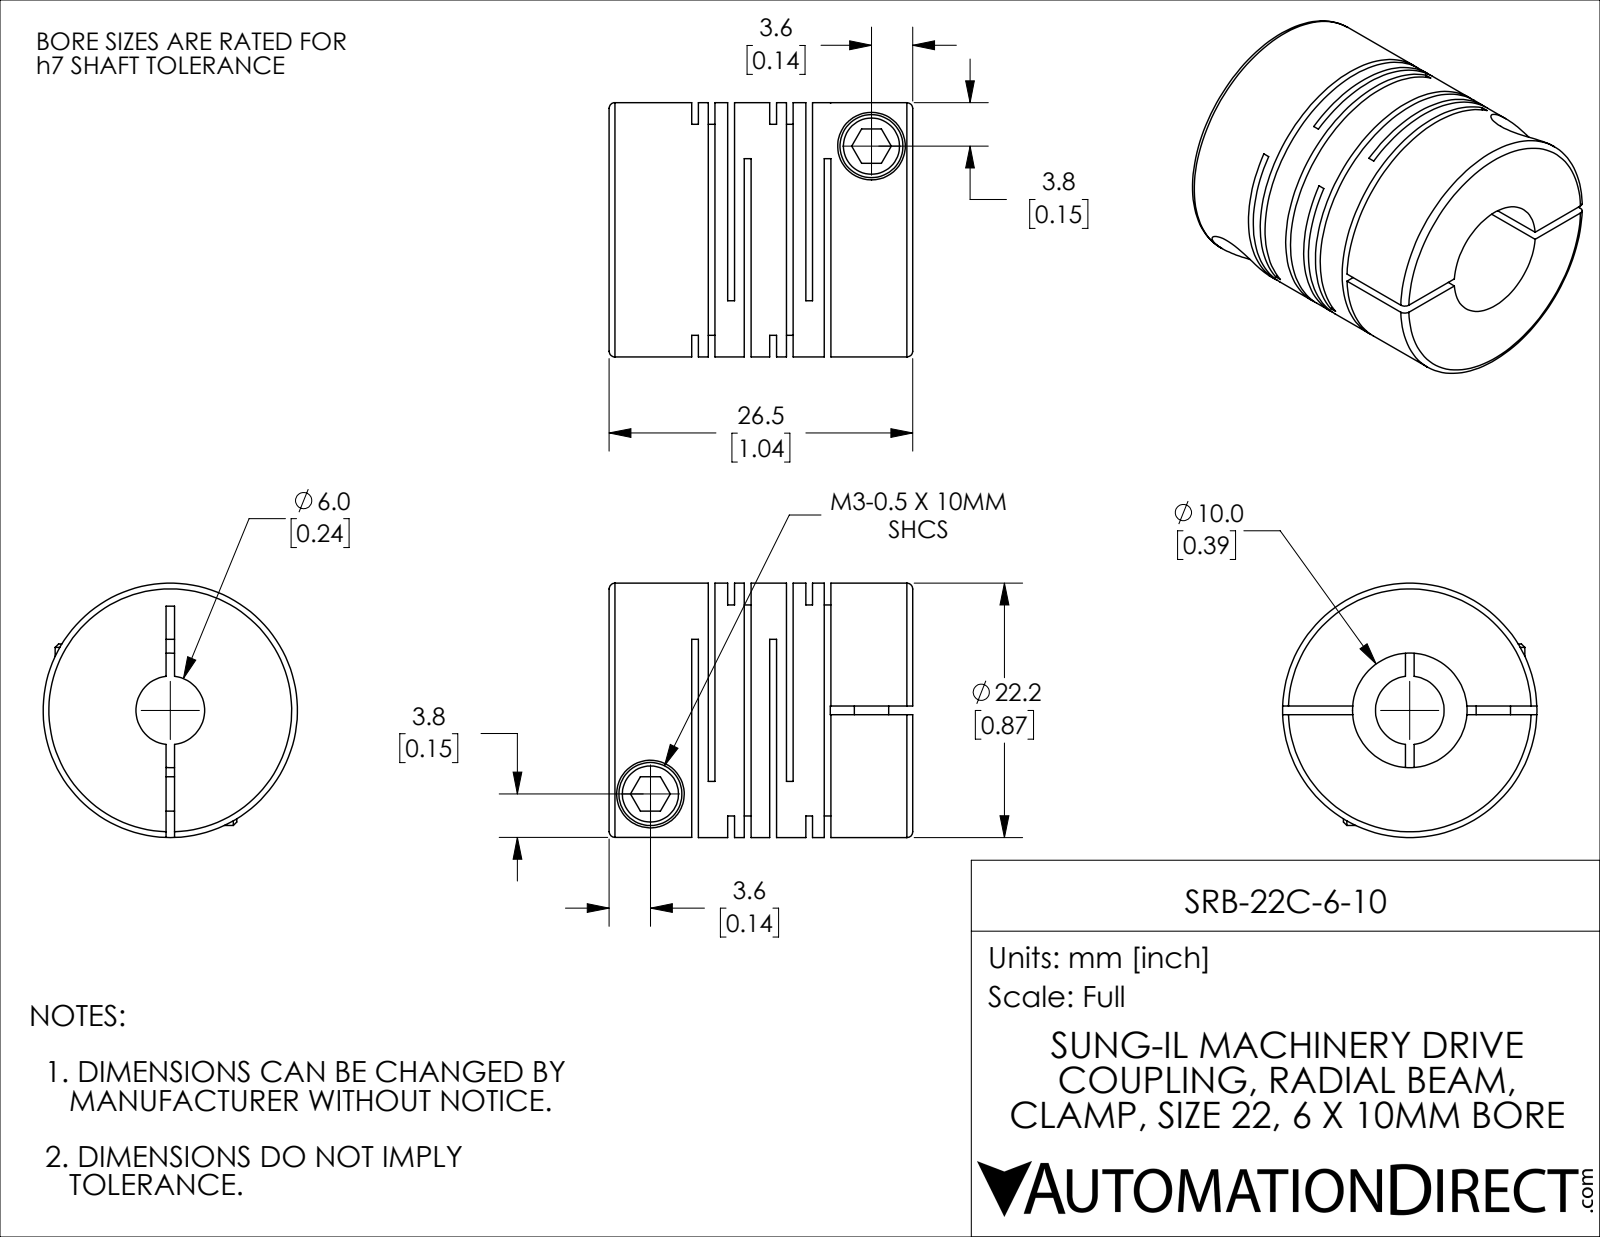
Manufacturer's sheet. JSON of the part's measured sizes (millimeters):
{"part_name": "SRB-22C-6-10", "step_written_by": "SolidWorks 2021 (CONFIG_CONTROL_DESIGN)", "units": "millimeters", "bodies": {"solids": 1, "faces": 115, "planar": 60, "cylindrical": 42, "other": 13}, "overall_size": [26.5, 22.2, 22.2], "volume_mm3": 7057, "surface_area_mm2": 7498, "round_holes": [[3, 2], [5.9, 2], [6, 1], [10, 1]], "round_bosses_or_shafts": [[5.5, 2], [22.2, 1]], "face_to_face_distances": [0.59, 3.15, 6.82, 1.45, 5.37, 3.67, 1.7, 2.04, 3.74, 7.41]}
